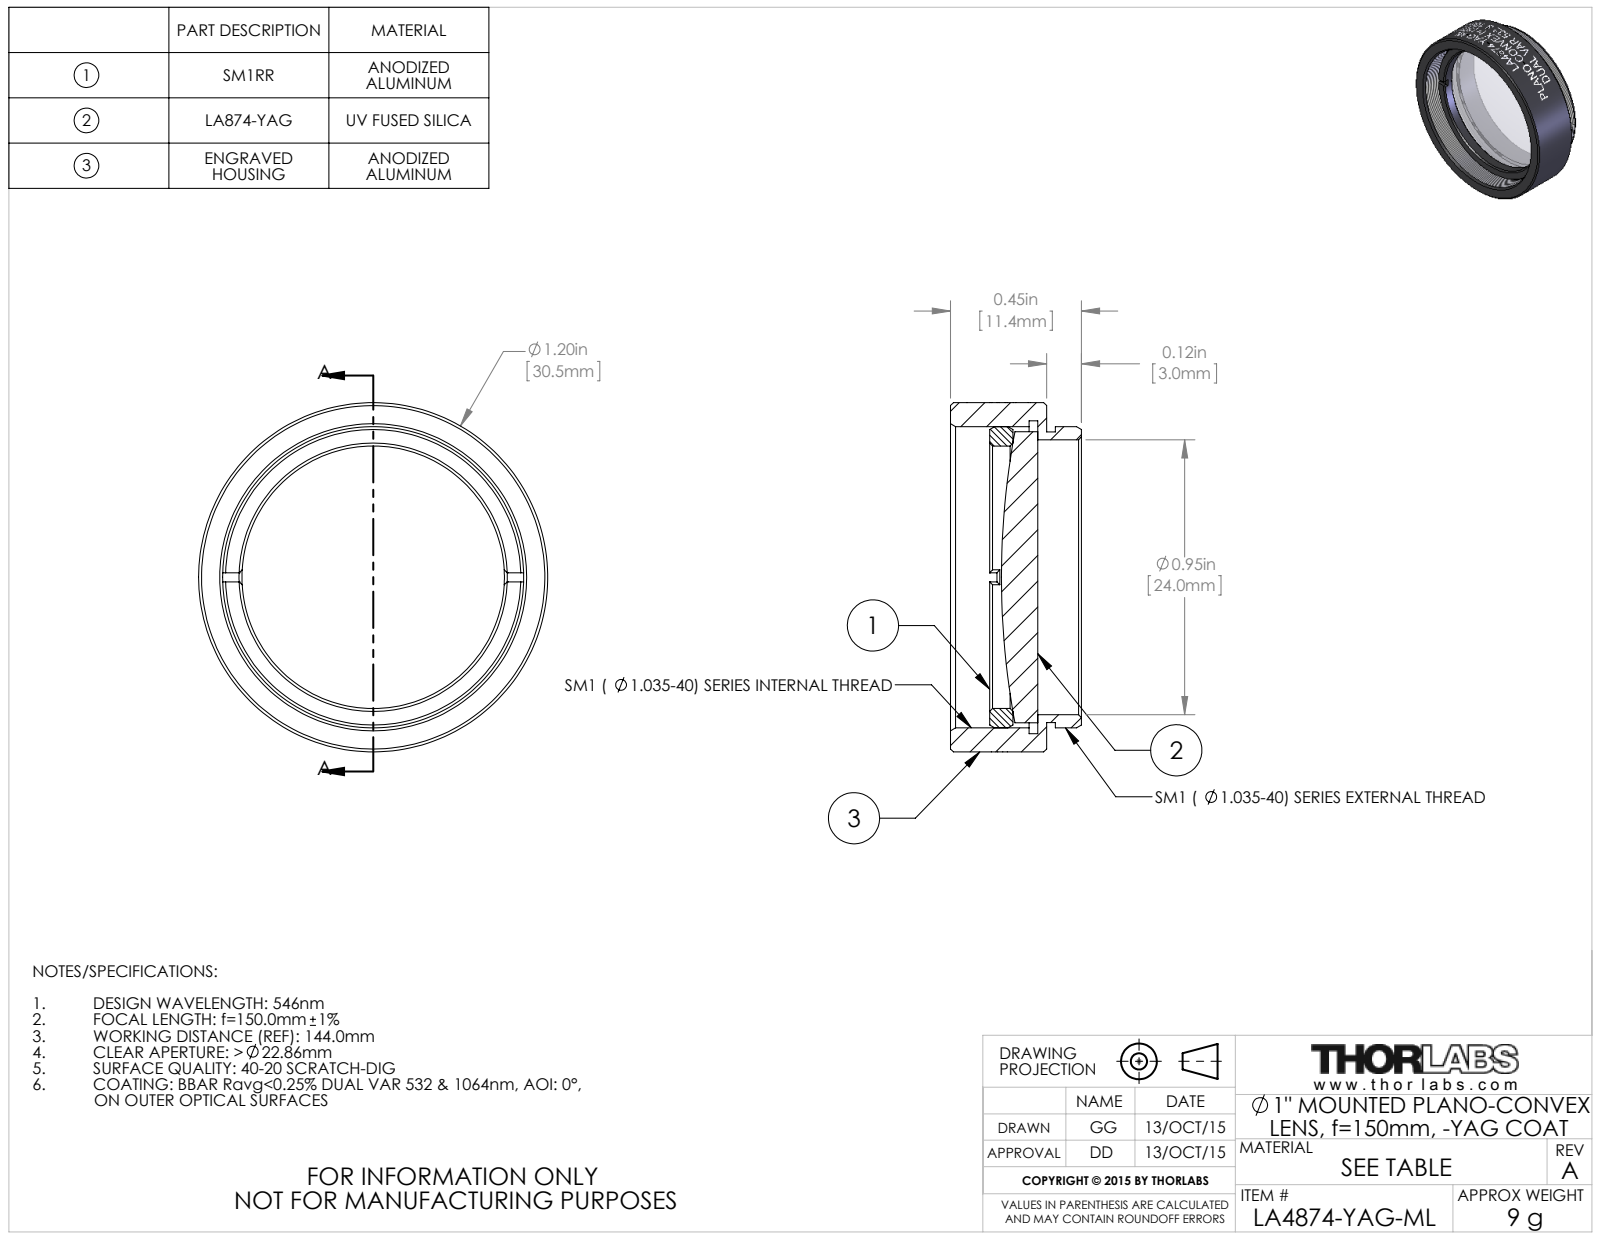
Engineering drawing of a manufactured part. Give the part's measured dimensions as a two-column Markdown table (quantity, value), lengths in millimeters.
| quantity | value |
| --- | --- |
| part name | TTN039426-E0W |
| STEP written by | SolidWorks 2014 (CONFIG_CONTROL_DESIGN) |
| units | millimeters |
| bodies | 3 solids, 155 faces (20 planar, 111 cylindrical, 24 other) |
| overall size | 30.48 × 30.48 × 11.43 |
| volume | 3 395 mm³ |
| surface area | 4 317 mm² |
| round holes (diameter × count) | 22.91 × 1, 24 × 1, 26.29 × 1, 27.31 × 1 |
| round bosses / shafts (diameter × count) | 30.48 × 1, 26.29 × 1, 25.4 × 1, 25.37 × 1 |
| main face-to-face distances | 0.76, 8.38, 7.62, 2.94, 2.18, 5.44, 4.98, 4.22, 2.04, 3.4 |
